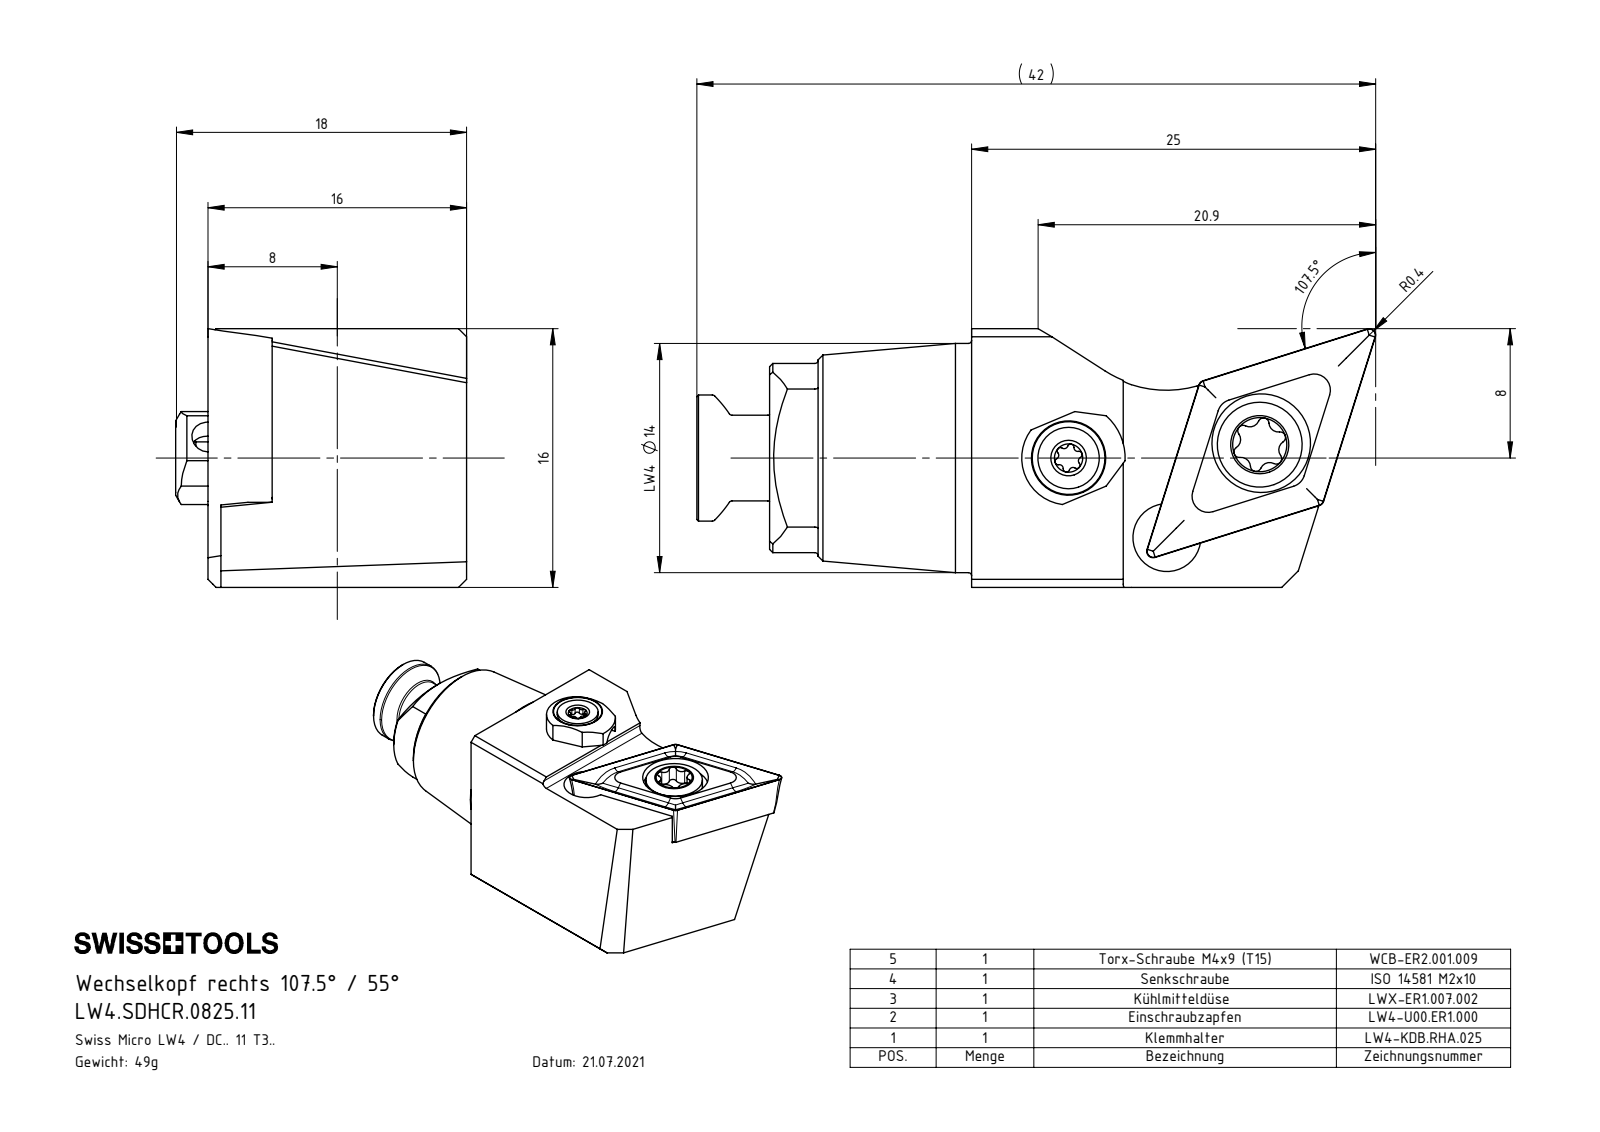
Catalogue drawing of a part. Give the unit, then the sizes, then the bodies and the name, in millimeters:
Units: millimetres
Overall size (bounding box): 42.01 × 18 × 16
Round holes (diameter × count): ⌀2 ×2, ⌀1.6 ×1, ⌀2.5 ×1, ⌀3 ×1, ⌀3.3 ×1, ⌀4.2 ×1, ⌀4.4 ×1, ⌀5.5 ×1, ⌀6.1 ×1
Round bosses / shafts (diameter × count): ⌀14.17 ×1, ⌀7.7 ×1, ⌀6 ×1, ⌀5.3 ×1, ⌀5.25 ×1, ⌀5 ×1, ⌀4 ×1, ⌀3.8 ×1
Partial cylindrical surfaces — rounded edges, fillets, slot ends (radius × count): R0.2 ×8, R0.24 ×6, R0.34 ×6, R0.59 ×6, R0.5 ×1, R1 ×1, R2.9 ×1, R3.5 ×1
Main face-to-face distances: 16, 12.03, 3.97, 7.5, 15.2, 3.17, 0.8, 2, 3, 12.5
Hole centre spacings: 7.51, 8.13, 8.26, 11.46, 11.56
Volume: 6 049 mm³ · Surface area: 3 792 mm²
Bodies: 6 solids, 264 faces (70 planar, 83 cylindrical, 111 other)
Part name (STEP PRODUCT): ISO 14581 - M2x10; WCB-ER2.001.009_A; DCMT11T304; LW4.SDHCR.0825.11 (+3 more)
STEP written by: SolidWorks 2022 (CONFIG_CONTROL_DESIGN)
